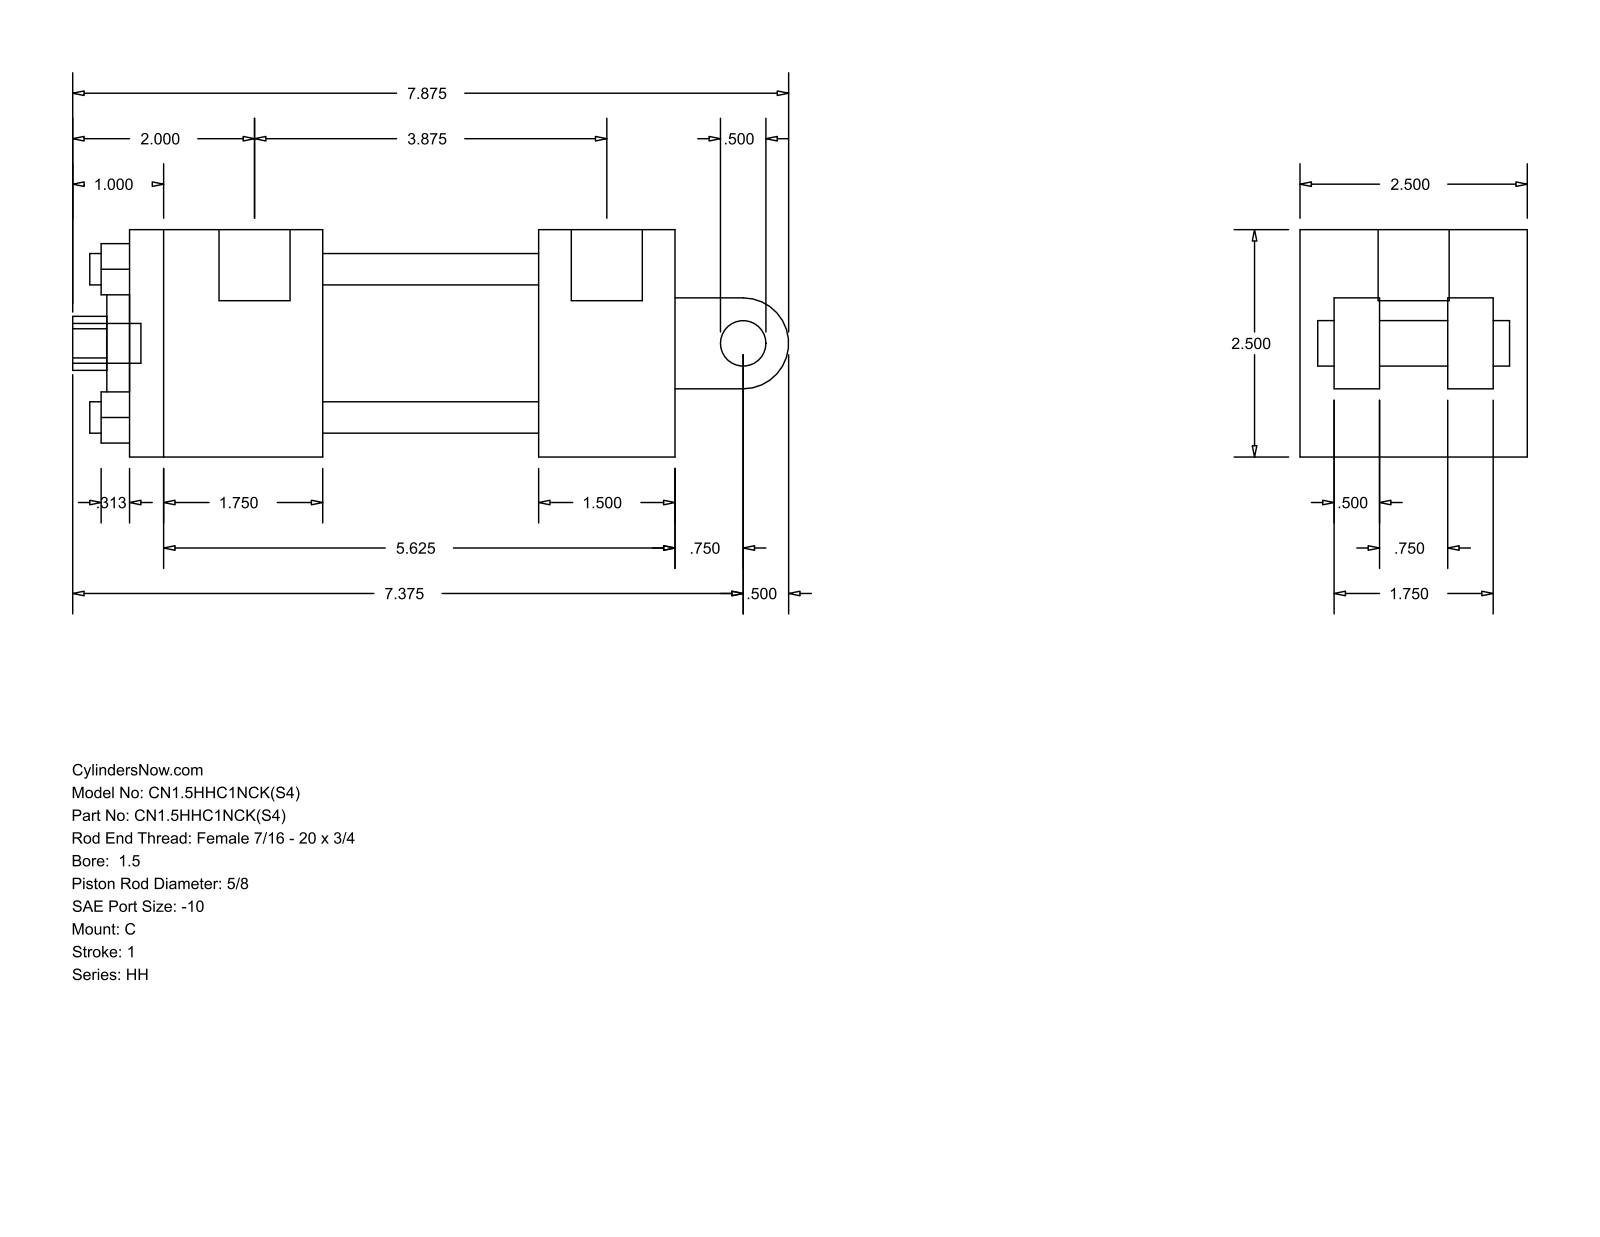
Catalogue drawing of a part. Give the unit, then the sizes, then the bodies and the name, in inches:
Units: inches
Overall size (bounding box): 7.875 × 2.5 × 2.5
Round holes (diameter × count): ⌀0.345 ×4, ⌀0.219 ×2, ⌀0.625 ×1, ⌀0.781 ×1, ⌀1.125 ×1, ⌀1.75 ×1
Round bosses / shafts (diameter × count): ⌀0.219 ×2, ⌀0.781 ×1, ⌀0.5 ×1, ⌀0.437 ×1
Partial cylindrical surfaces — rounded edges, fillets, slot ends (radius × count): R0.297 ×1, R0.5 ×1
Main face-to-face distances: 2.5, 6, 1.5, 2.125, 4.5, 2.375, 3.875, 0.5, 0.375, 0.75
Hole centre spacings: 1.152, 1.63, 2.305, 0.063
Bodies: 0 solids, 99 faces (70 planar, 29 cylindrical, 0 other)
Part name (STEP PRODUCT): HH_C__0150_0.625
STEP written by: GSSL Pune (CONFIG_CONTROL_DESIGN)
